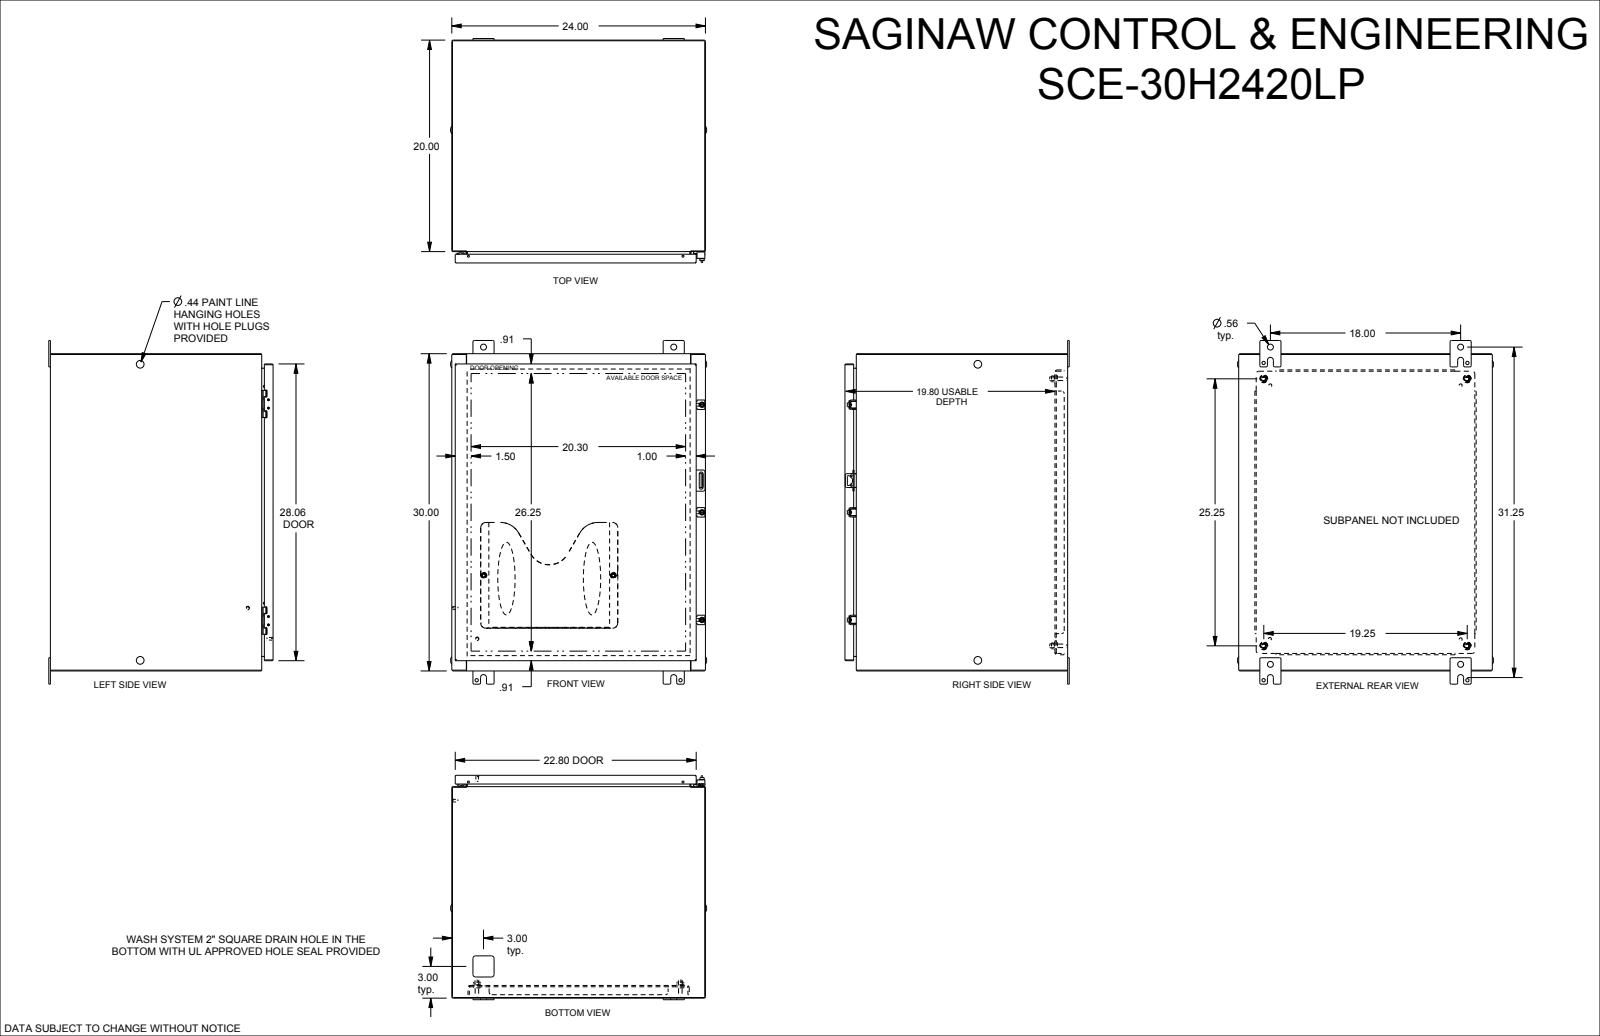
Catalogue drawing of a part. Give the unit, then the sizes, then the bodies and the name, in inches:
Units: inches
Overall size (bounding box): 32.5 × 24.236 × 21.222
Round holes (diameter × count): ⌀0.25 ×6, ⌀0.158 ×4, ⌀0.166 ×4, ⌀0.172 ×4, ⌀0.21 ×4, ⌀0.244 ×4, ⌀0.266 ×4, ⌀0.281 ×4, ⌀0.313 ×4, ⌀0.367 ×4, ⌀0.5 ×4, ⌀0.563 ×4
Round bosses / shafts (diameter × count): ⌀0.248 ×8, ⌀0.25 ×7, ⌀0.563 ×6, ⌀0.366 ×4, ⌀0.332 ×4, ⌀0.17 ×4, ⌀0.507 ×3, ⌀0.196 ×3
Partial cylindrical surfaces — rounded edges, fillets, slot ends (radius × count): R0.01 ×124, R0.015 ×47, R0.029 ×36, R0.06 ×32, R0.125 ×32, R0.045 ×17, R0.05 ×13, R0.031 ×12
Main face-to-face distances: 0.075, 23.925, 29.925, 20.998, 20.923, 0.075, 21.073, 20.998, 1.2, 19.873
Hole centre spacings: 20.5, 0.787, 2.35, 10.175, 10.188, 18.701, 19.713, 21.287
Bodies: 0 solids, 3620 faces (1473 planar, 779 cylindrical, 1368 other)
Part name (STEP PRODUCT): SCE-30H2420LP
STEP written by: SolidWorks 2019 (CONFIG_CONTROL_DESIGN)
